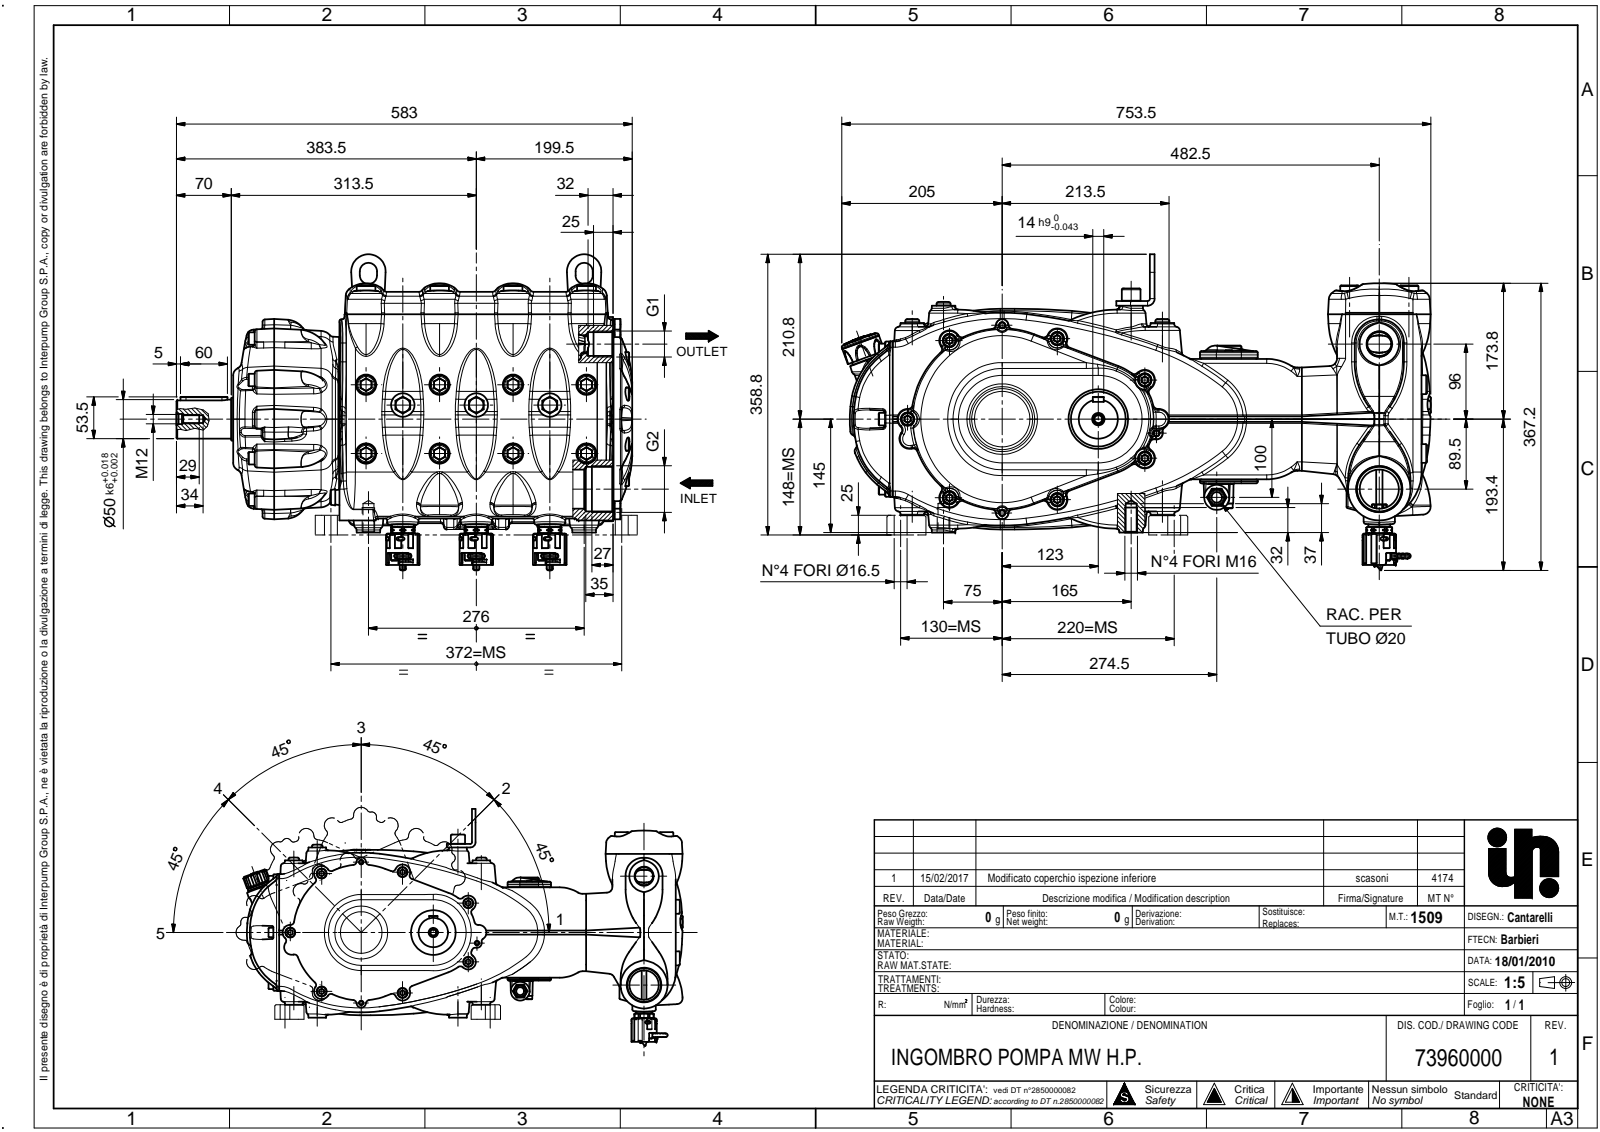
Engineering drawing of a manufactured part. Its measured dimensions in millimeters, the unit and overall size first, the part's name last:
Units: millimetres
Overall size (bounding box): 753.75 × 582.99 × 404.19
Round holes (diameter × count): ⌀14 ×25, ⌀17 ×23, ⌀8.5 ×19, ⌀16.5 ×10, ⌀5 ×8, ⌀8 ×8, ⌀11 ×8, ⌀25 ×8, ⌀26 ×8, ⌀10.5 ×7, ⌀3 ×6, ⌀3.5 ×6
Round bosses / shafts (diameter × count): ⌀16 ×39, ⌀10 ×29, ⌀24 ×18, ⌀18 ×8, ⌀16.8 ×6, ⌀27 ×5, ⌀40 ×4, ⌀30 ×4
Partial cylindrical surfaces — rounded edges, fillets, slot ends (radius × count): R0.5 ×884, R2 ×145, R0.3 ×120, R0.2 ×86, R0.14 ×62, R4 ×57, R1.5 ×56, R1 ×42
Main face-to-face distances: 523.5, 0.5, 350.5, 350, 433.5, 83.5, 339.66, 57, 211, 154
Hole centre spacings: 94, 88, 188, 60.44, 84.01, 103.51, 118.8, 146.03
Volume: 61 890 000 mm³ · Surface area: 2 739 000 mm²
Bodies: 188 solids, 13891 faces (3406 planar, 3352 cylindrical, 7133 other)
STEP written by: THINKDESIGN (AUTOMOTIVE_DESIGN)
